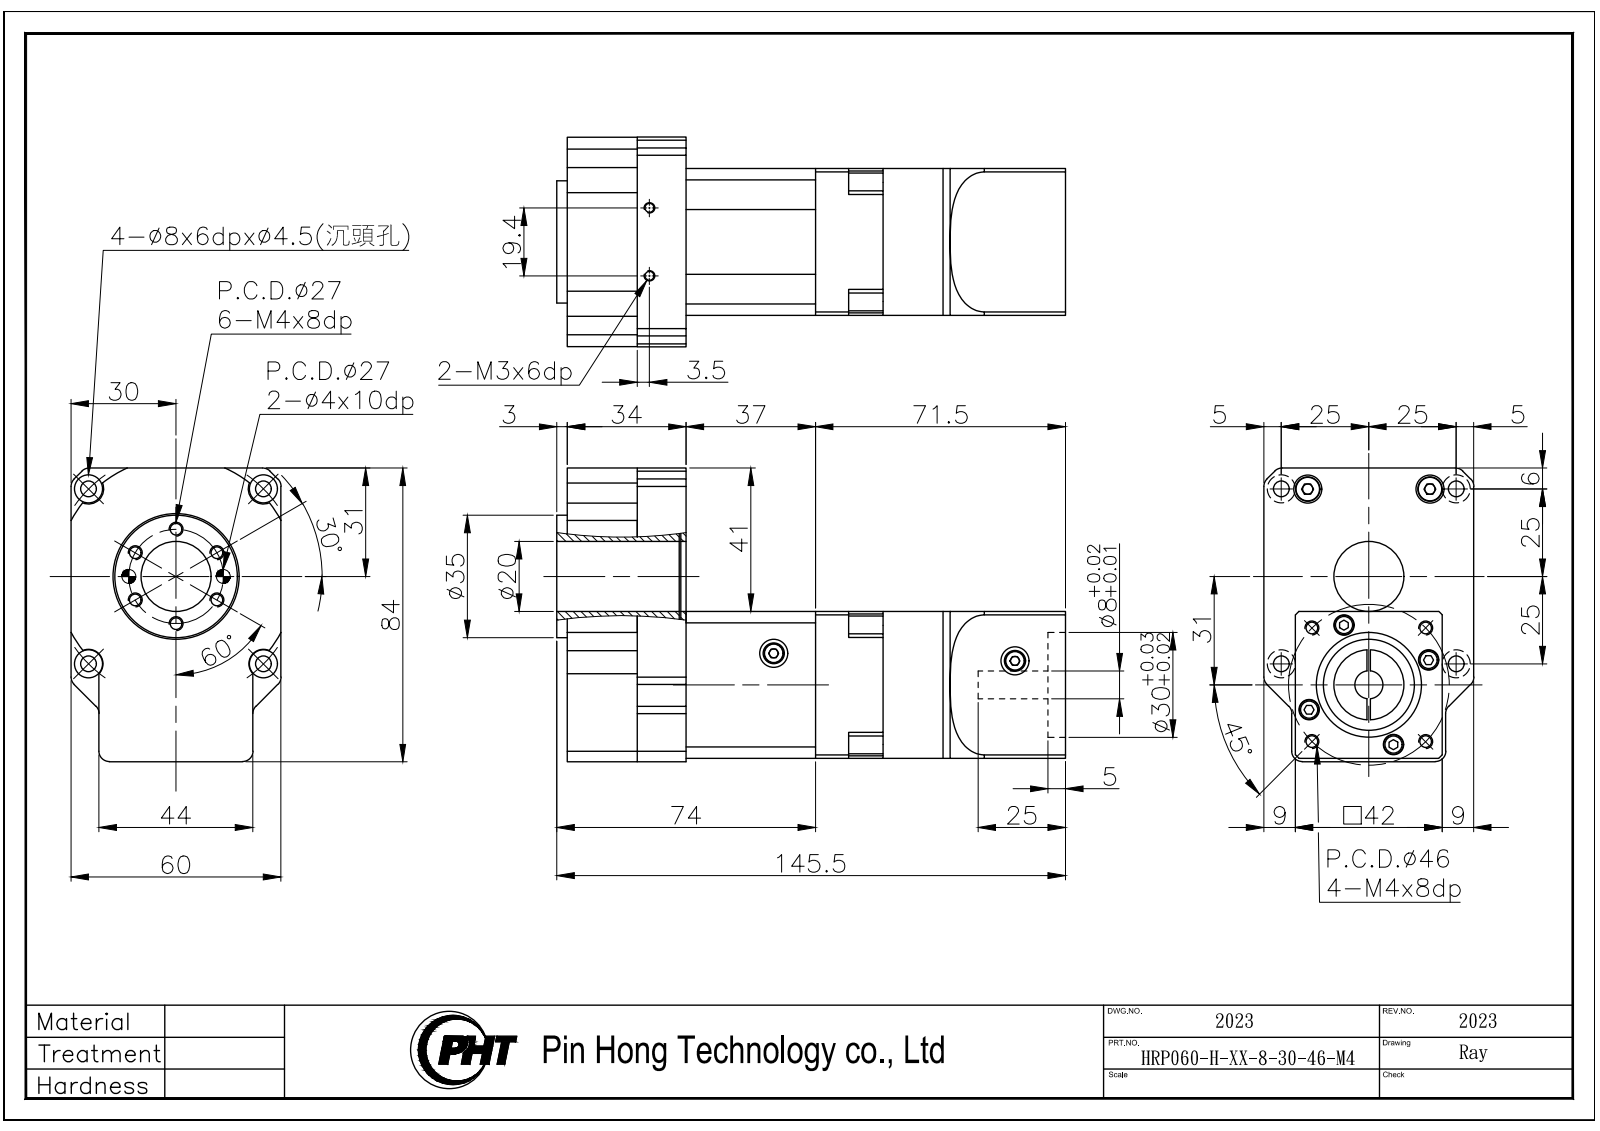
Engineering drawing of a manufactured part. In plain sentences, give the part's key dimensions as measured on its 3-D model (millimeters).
The part is named "HRP060-H-XX-8-30-46-M4_2023". Its 3-D file was written by "SolidWorks 2016 (CONFIG_CONTROL_DESIGN)". It is 3 solids with 512 faces: 213 planar, 241 cylindrical and 58 other. Overall it measures 145.5 by 84 by 60 millimeters. Its volume is 295 283 cubic millimeters and its surface area 64 311 square millimeters. Round holes: 15 of diameter 3.3, 11 of diameter 8, 10 of diameter 4.5, 4 of diameter 3.4, 4 of diameter 5.8, 4 of diameter 6, 3 of diameter 2.5, 2 of diameter 4, 2 of diameter 30, 1 of diameter 3.9, 1 of diameter 14, 1 of diameter 20. Round bosses or shafts: 8 of diameter 5.5, 2 of diameter 7, 1 of diameter 42, 1 of diameter 35, 1 of diameter 20, 1 of diameter 15, 1 of diameter 7.37. Partial cylindrical surfaces (rounded edges, fillets, slot ends): 13 of radius 3, 8 of radius 4, 4 of radius 4.05, 1 of radius 14, 1 of radius 25, 1 of radius 27.5, 1 of radius 29, 1 of radius 34. The main face-to-face distances are 42, 73.5, 37, 34, 107.5, 36.5, 71, 35, 51, 0.95. The hole center spacings are 13.5, 27.52, 45.9, 23.38, 48.52, 5.39, 6.99, 9.22.
